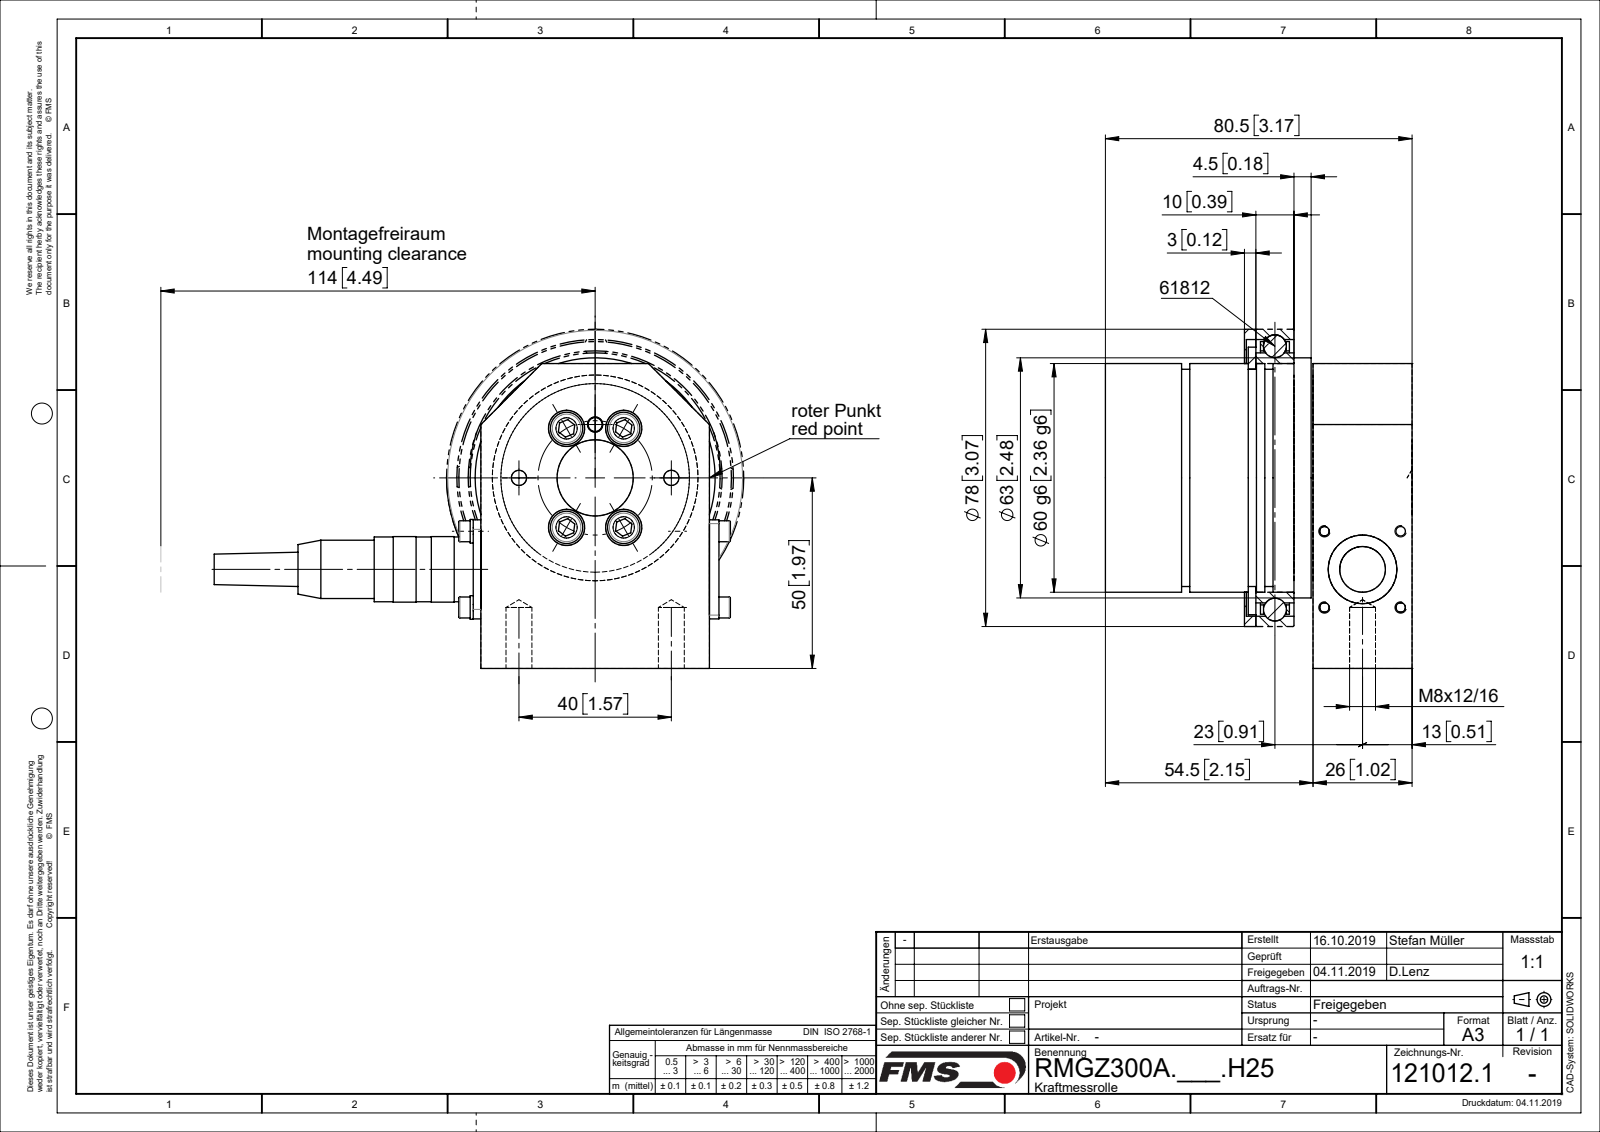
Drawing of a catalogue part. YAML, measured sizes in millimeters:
part_name: "R1210121; R51047; R1110253; I-6KT_SCHRAUBE_M5X8 (+8 more)"
step_written_by: "Mechanical Desktop 2009 (CONFIG_CONTROL_DESIGN)"
units: millimeters
bodies: {solids: 27, faces: 532, planar: 142, cylindrical: 262, other: 128}
overall_size: [140.5, 90.5, 80.5]
volume: 257561
surface_area: 96806
round_holes:
  - {diameter: 4, count: 5}
  - {diameter: 2.6, count: 4}
  - {diameter: 3.2, count: 4}
  - {diameter: 3.4, count: 4}
  - {diameter: 5.6, count: 4}
  - {diameter: 9, count: 4}
  - {diameter: 9.5, count: 4}
  - {diameter: 7.15, count: 2}
  - {diameter: 5, count: 1}
  - {diameter: 12, count: 1}
  - {diameter: 15, count: 1}
  - {diameter: 18, count: 1}
round_bosses_or_shafts:
  - {diameter: 1.5, count: 5}
  - {diameter: 8, count: 4}
  - {diameter: 5.5, count: 4}
  - {diameter: 5, count: 4}
  - {diameter: 3, count: 4}
  - {diameter: 81, count: 1}
  - {diameter: 78, count: 1}
  - {diameter: 68.6, count: 1}
partial_cylinders:
  - {radius: 1, count: 4}
  - {radius: 2.5, count: 4}
face_to_face_distances: [35, 12.5, 3, 32, 44, 17, 2.5, 47.5, 37.5, 0.5]
hole_center_spacings: [15, 14.14, 20, 7.57, 25.98, 28.01, 28.28, 30]
